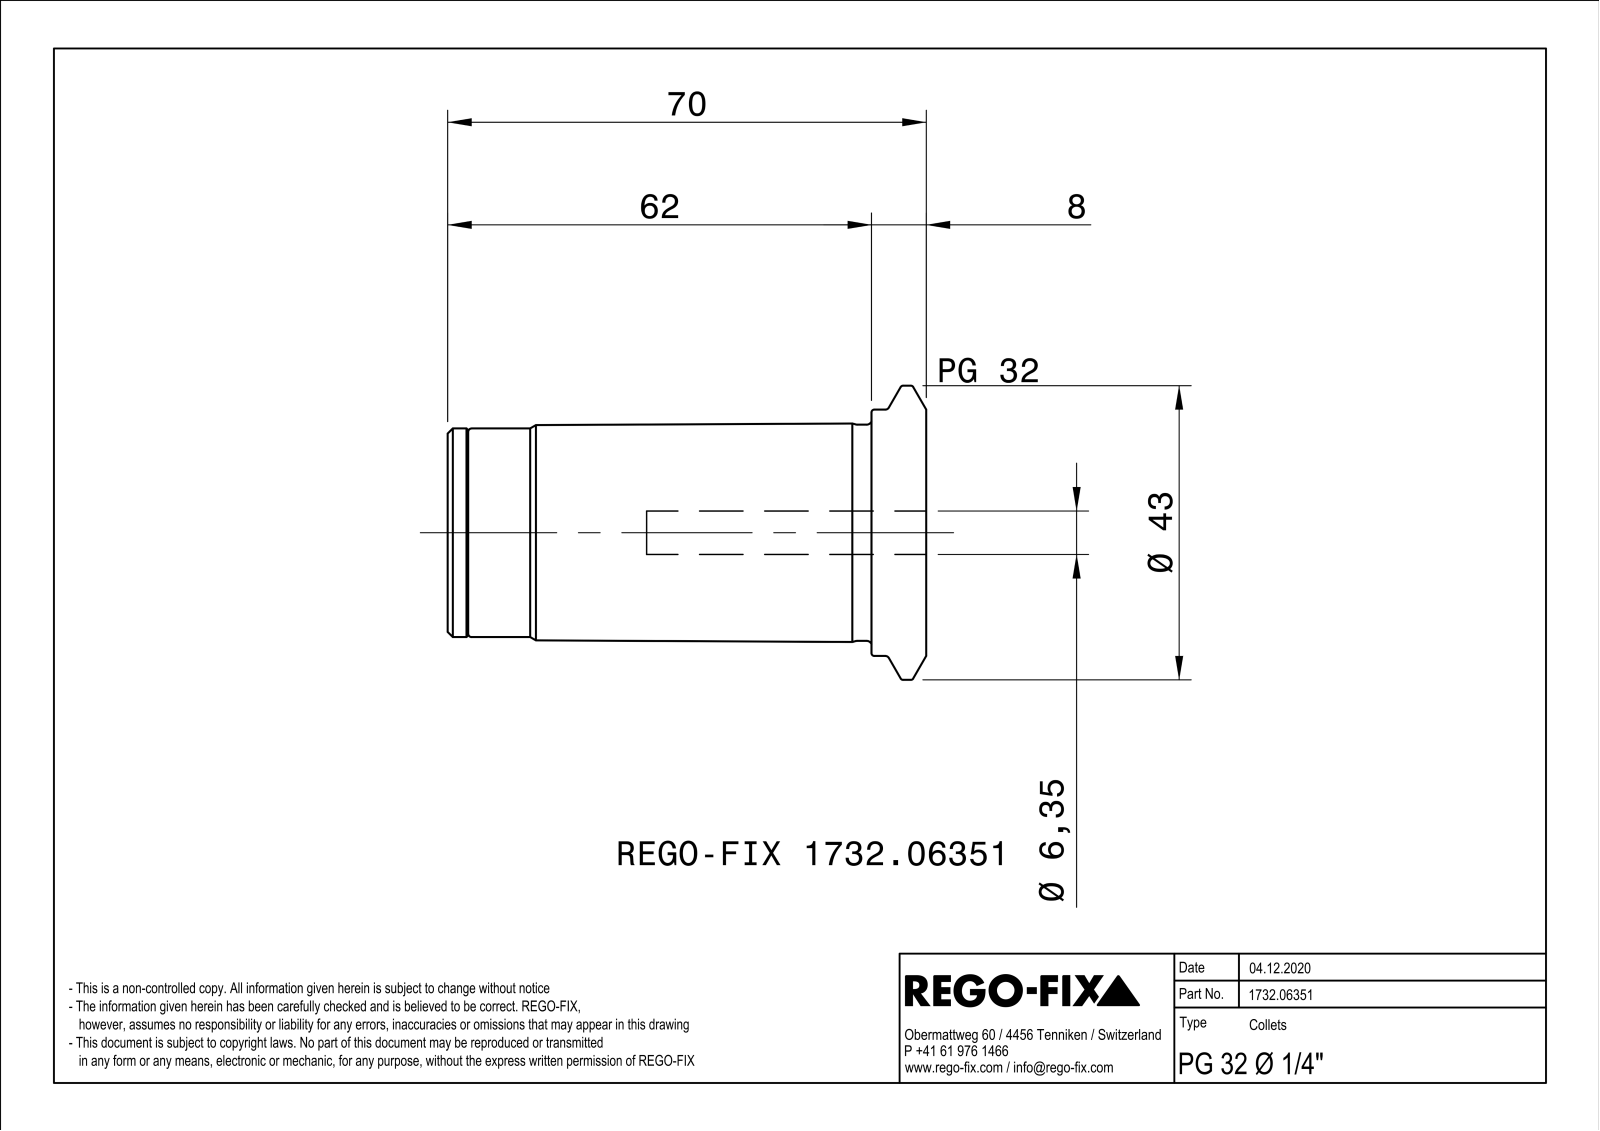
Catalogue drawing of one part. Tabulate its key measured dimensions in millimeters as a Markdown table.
| quantity | value |
| --- | --- |
| part name | NOCUT |
| STEP written by | SIEMENS PLM Software Solid Edge ST10 (AUTOMOTIVE_DESIGN) |
| units | millimeters |
| bodies | 1 solid, 127 faces (31 planar, 41 cylindrical, 55 other) |
| overall size | 70 × 43 × 42.99 |
| volume | 48 378 mm³ |
| surface area | 16 597 mm² |
| round holes (diameter × count) | 4 × 3, 6.35 × 1, 8.92 × 1, 10.5 × 1, 15.5 × 1, 26.92 × 1, 28.5 × 1 |
| round bosses / shafts (diameter × count) | 43 × 1, 36 × 1, 31.6 × 1, 30.5 × 1, 26.5 × 1, 21 × 1 |
| partial cylindrical surfaces (radius × count) | 2 × 6, 3.5 × 3, 3.98 × 1, 4.75 × 1, 8.75 × 1 |
| main face-to-face distances | 1, 70, 58, 12, 59, 11, 8, 60, 2, 10 |
| hole center spacings | 7.75, 13.42, 13.43 |
